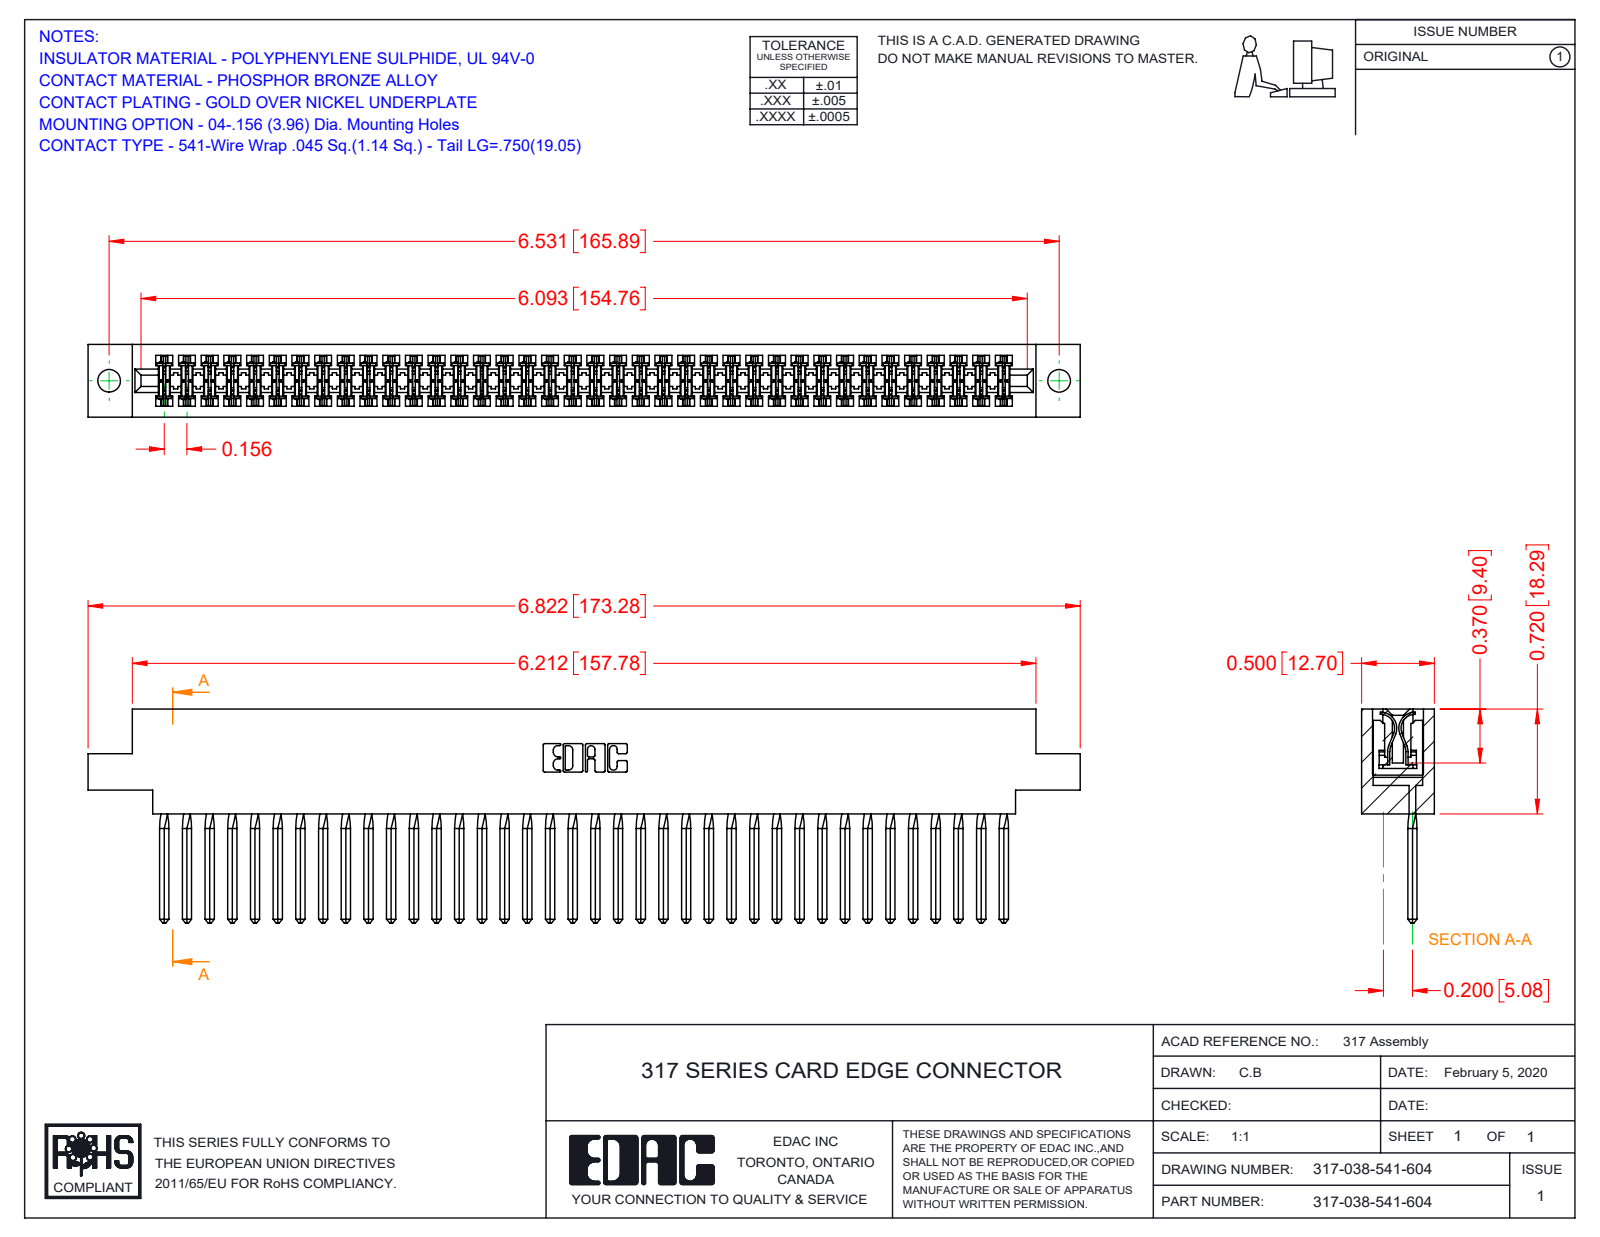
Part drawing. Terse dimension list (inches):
name: 317-038-541-604; 317-290-002_541; 317 Part_.156 Dia - TH
written by: SolidWorks 2016 (CONFIG_CONTROL_DESIGN)
unit: in
bodies: 39 solids, 5878 faces (4770 planar, 956 cylindrical, 152 other)
size: 6.822 × 1.47 × 0.5
volume: 1.702 in³; area: 60.6 in²
holes: 2× ⌀0.156
rounds: 76× R0.015, 22× R0.01, 6× R0.007, 6× R0.031, 3× R0.026, 2× R0.095, 2× R0.1, 2× R0.11
face distances: 0.5, 0.075, 0.425, 0.35, 0.195, 0.11, 0.72, 0.115, 0.211, 0.289
hole spacings: 6.531
